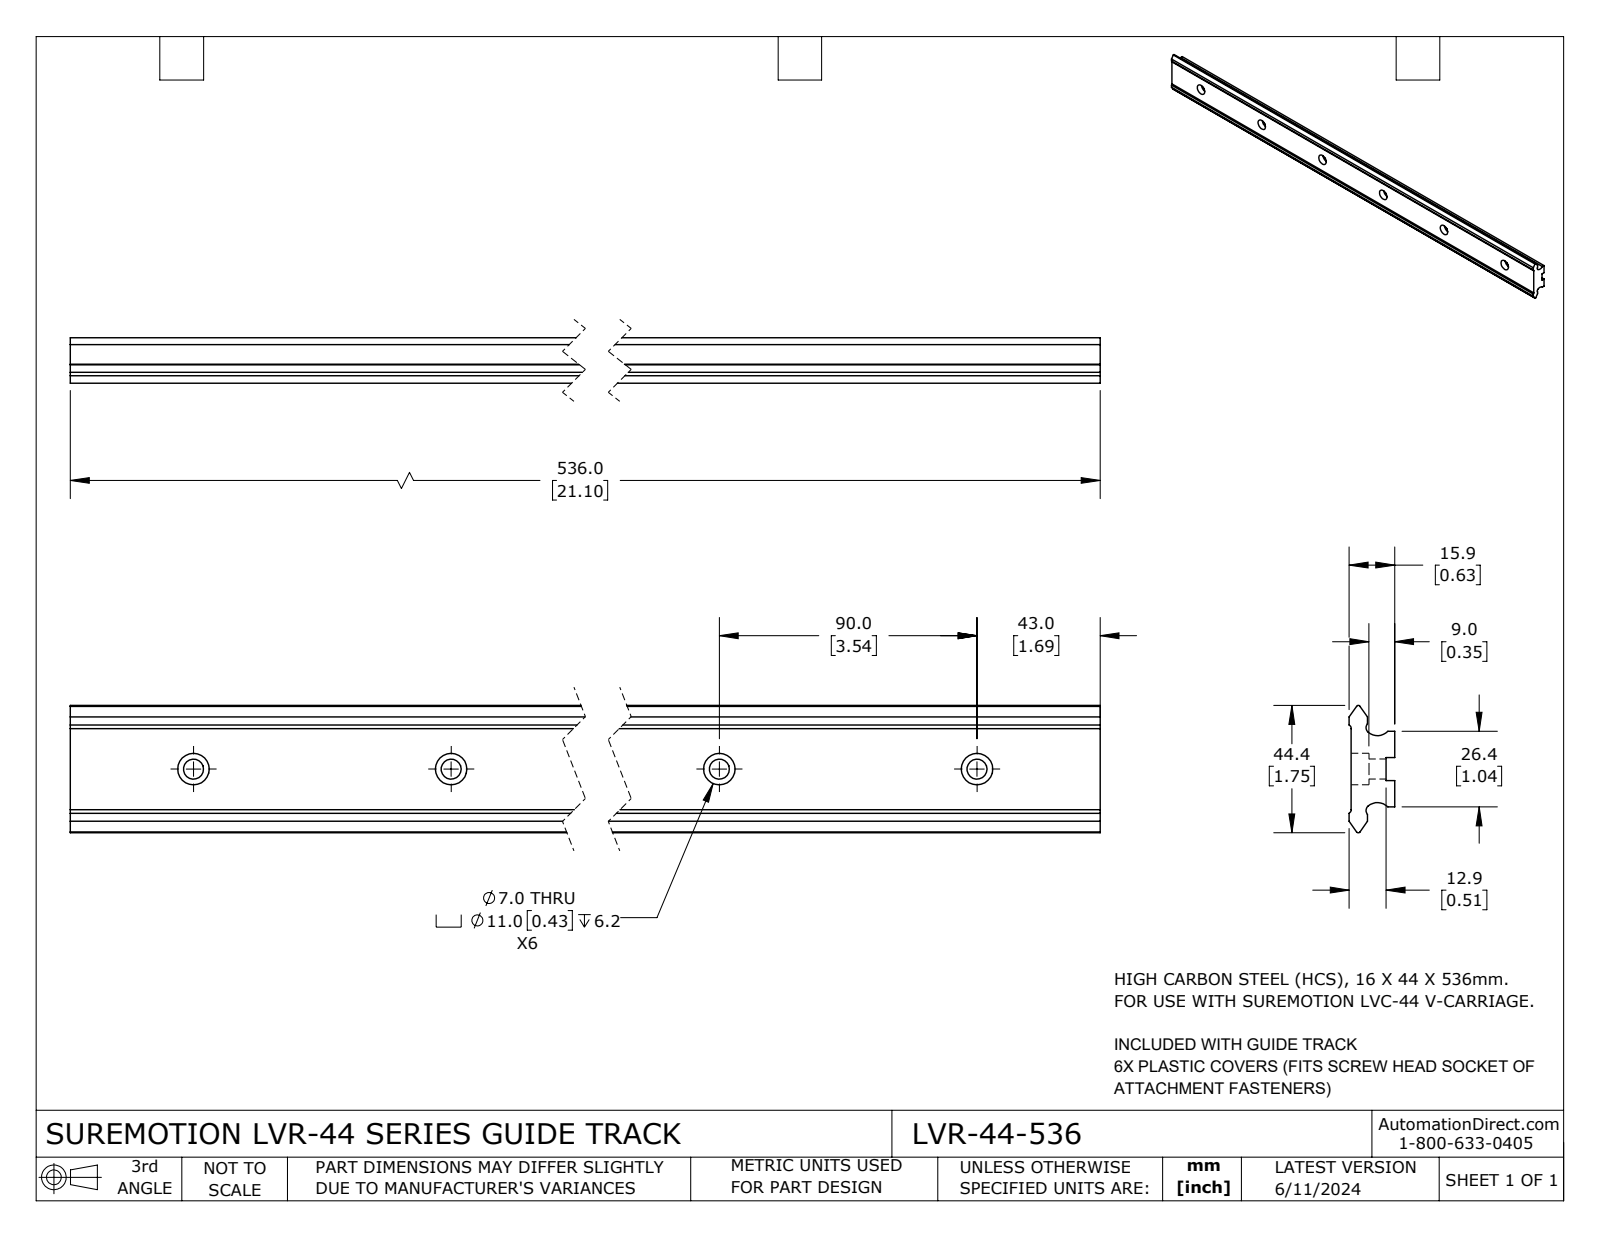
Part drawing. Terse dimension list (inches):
name: LVR-44-536
written by: SolidWorks 2023 (CONFIG_CONTROL_DESIGN)
unit: in
bodies: 1 solid, 58 faces (24 planar, 34 cylindrical, 0 other)
size: 21.102 × 1.75 × 0.626
volume: 14.45 in³; area: 104.9 in²
holes: 6× ⌀0.276, 6× ⌀0.433
rounds: 2× R0.03, 2× R0.059, 2× R0.084, 2× R0.196
face distances: 0.598, 1.03, 0.118, 0.48, 0.626, 0.508, 0.028, 0.362, 0.677, 0.373
hole spacings: 3.543, 7.087, 10.63, 14.173, 17.717
